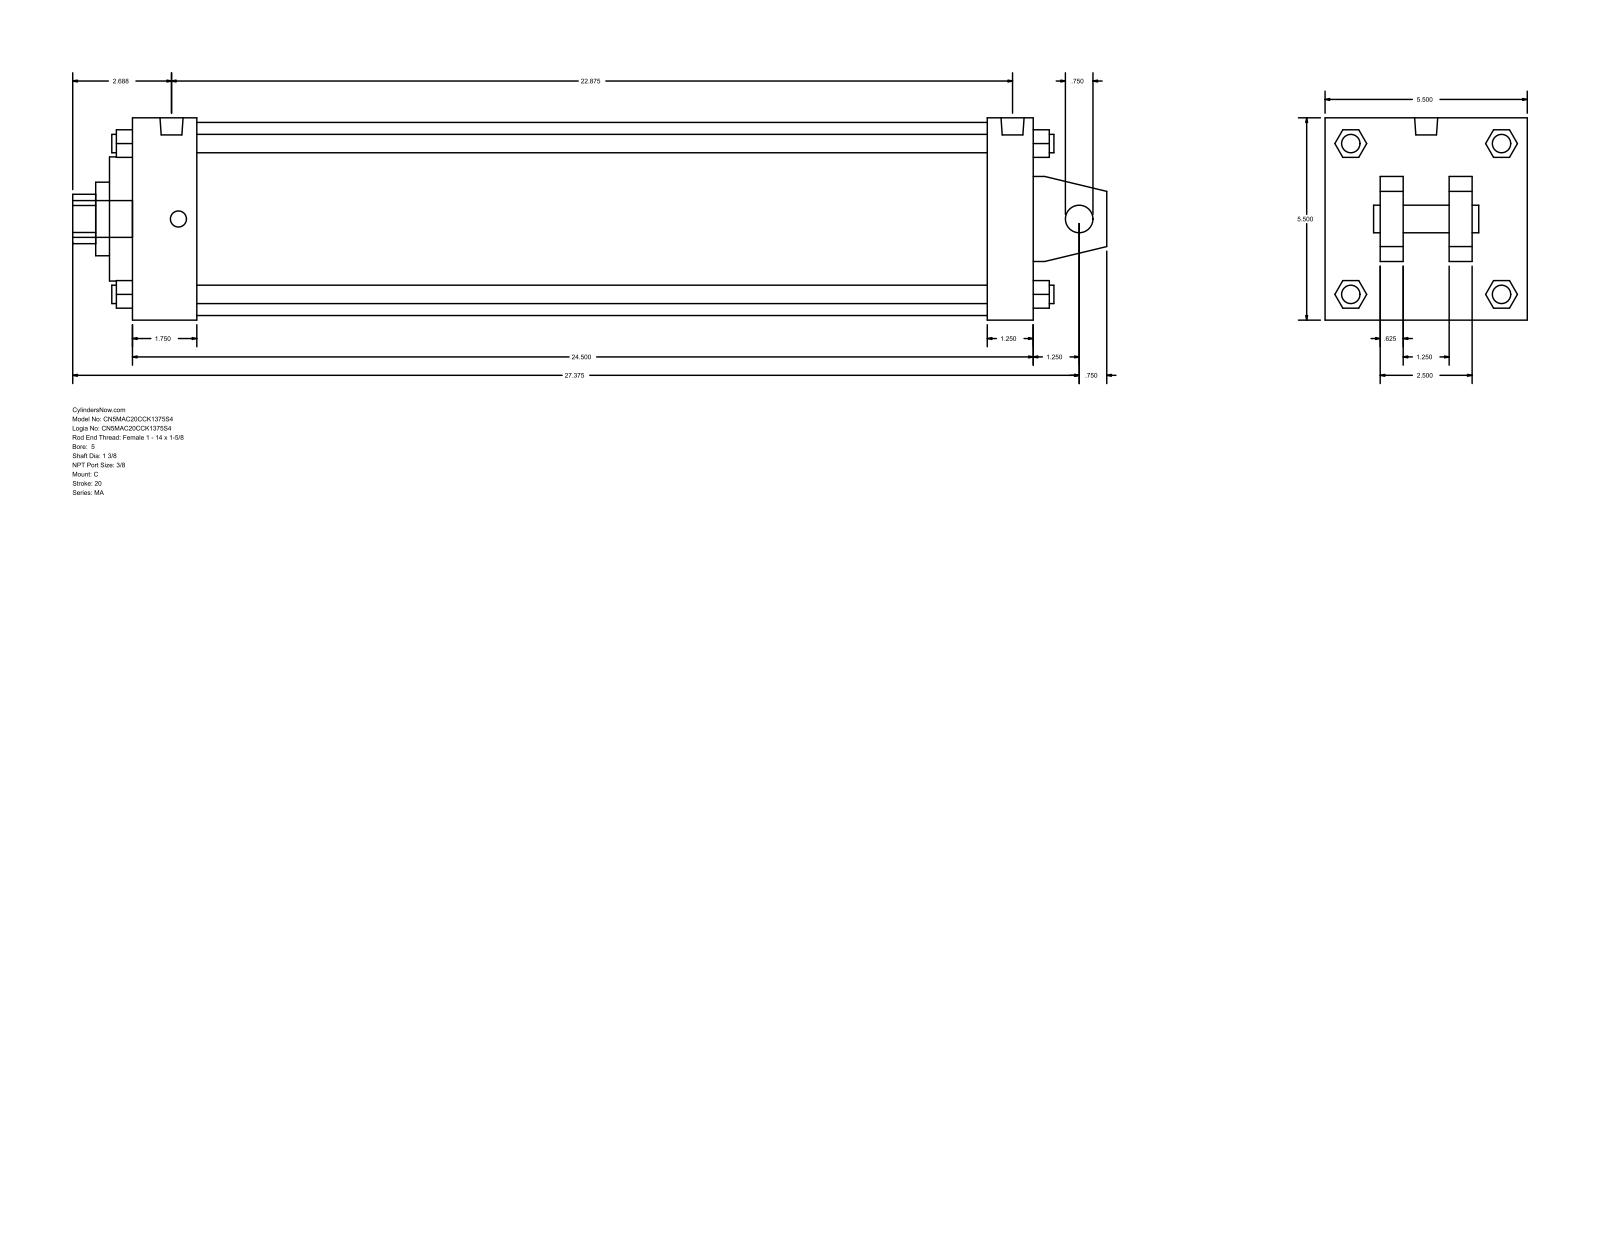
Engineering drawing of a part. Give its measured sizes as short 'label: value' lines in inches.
name: MA_C__0500_1.375
written by: GSSL Pune (CONFIG_CONTROL_DESIGN)
unit: in
bodies: 0 solids, 141 faces (109 planar, 32 cylindrical, 0 other)
size: 28.125 × 5.5 × 5.5
holes: 1× ⌀0.75, 1× ⌀1.375, 1× ⌀2, 1× ⌀3.375, 1× ⌀5.25
bosses: 4× ⌀0.5, 4× ⌀0.437, 2× ⌀0.627, 1× ⌀1
rounds: 1× R0.672
face distances: 5.5, 24.5, 0.625, 23.25, 1.25, 1.75, 21.5, 22.75, 1.5, 4
